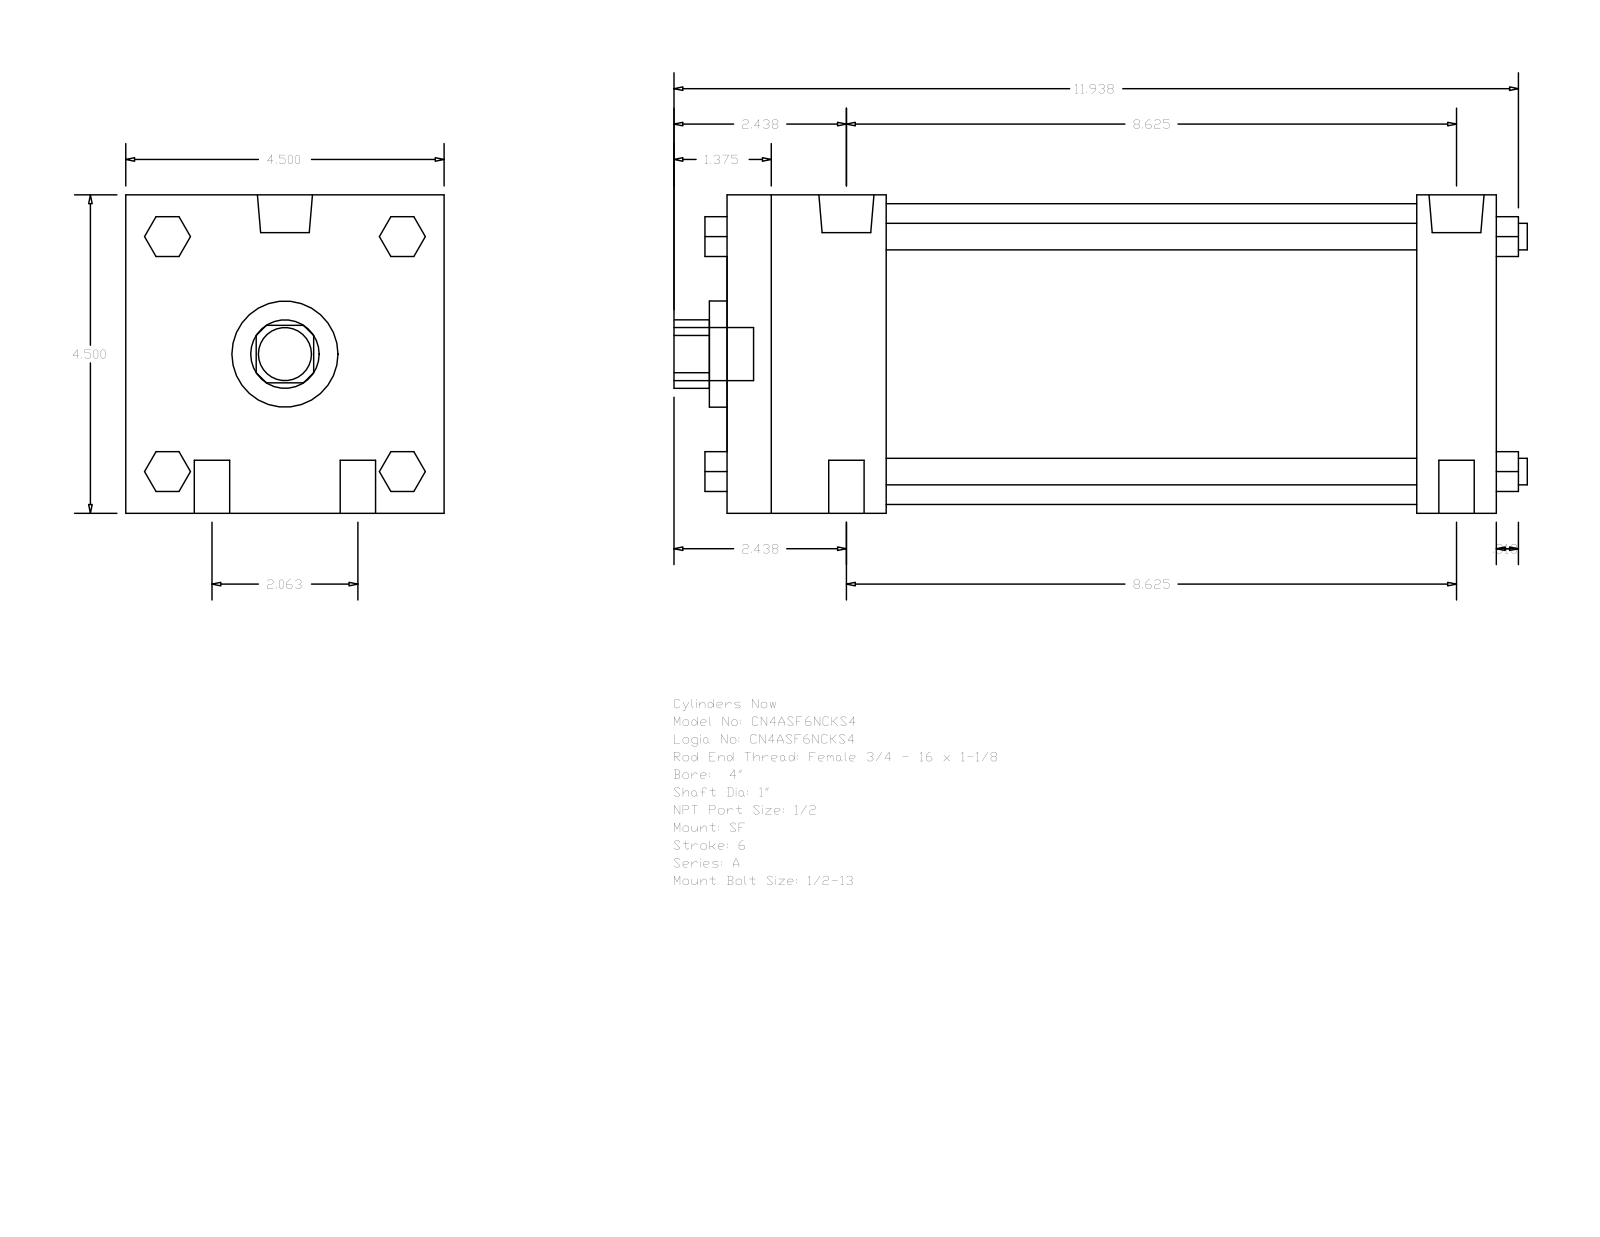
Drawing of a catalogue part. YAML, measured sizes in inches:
part_name: "A_SF__0400_1"
step_written_by: "GSSL Pune (CONFIG_CONTROL_DESIGN)"
units: inches
bodies: {solids: 0, faces: 124, planar: 94, cylindrical: 30, other: 0}
overall_size: [12.063, 4.5, 4.5]
round_holes:
  - {diameter: 1, count: 1}
  - {diameter: 1.5, count: 1}
  - {diameter: 4.25, count: 1}
round_bosses_or_shafts:
  - {diameter: 0.5, count: 4}
  - {diameter: 0.375, count: 4}
  - {diameter: 0.778, count: 2}
  - {diameter: 0.344, count: 2}
  - {diameter: 0.75, count: 1}
partial_cylinders:
  - {radius: 0.484, count: 1}
face_to_face_distances: [4.5, 10.875, 1.125, 9.75, 2.25, 7.5, 8.625, 0.563, 1.66, 2.875]
